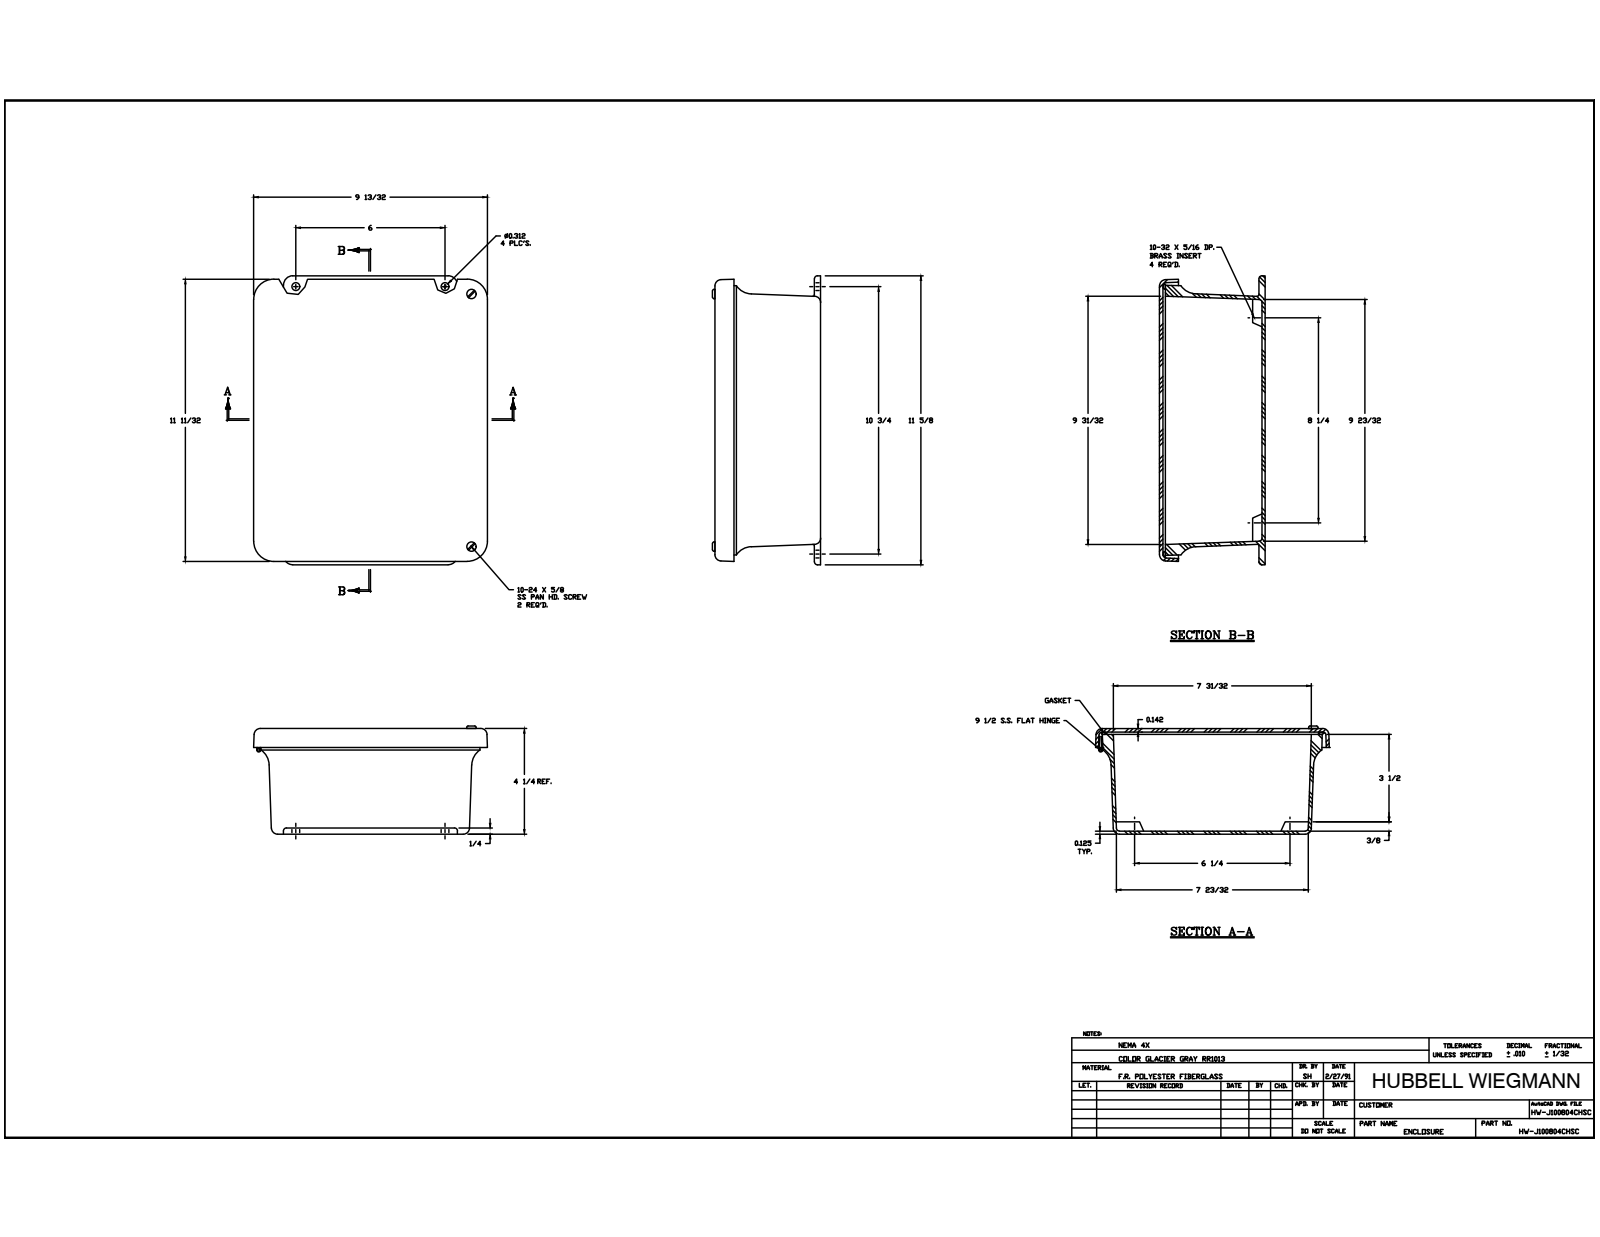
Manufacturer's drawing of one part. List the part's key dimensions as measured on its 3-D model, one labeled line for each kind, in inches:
Part name (STEP PRODUCT): J1008HW_2; RMINS45821P_23; RMINS45821P_24; RMINS45821P_25 (+8 more)
STEP written by: Autodesk Inventor 2014 (AUTOMOTIVE_DESIGN)
Units: inches
Bodies: 22 solids, 759 faces (259 planar, 291 cylindrical, 209 other)
Overall size (bounding box): 11.625 × 9.433 × 4.366
Volume: 60.58 in³ · Surface area: 805.5 in²
Round holes (diameter × count): ⌀0.131 ×8, ⌀0.14 ×8, ⌀0.152 ×5, ⌀0.156 ×4, ⌀0.218 ×4, ⌀0.145 ×2, ⌀0.085 ×1, ⌀0.085 ×1
Round bosses / shafts (diameter × count): ⌀0.25 ×8, ⌀0.125 ×8, ⌀0.27 ×6, ⌀0.19 ×2, ⌀0.156 ×2, ⌀0.155 ×1
Partial cylindrical surfaces — rounded edges, fillets, slot ends (radius × count): R0.031 ×20, R0.125 ×12, R0.25 ×8, R0.2 ×7, R0.375 ×4, R0.75 ×4, R0.063 ×2
Main face-to-face distances: 0.142, 4.093, 4.235, 0.125, 3.968, 4.11, 0.12, 3.89, 0.22, 4.015
Hole centre spacings: 6, 3, 0.25, 2.5, 2.75, 6.25, 1.337, 3.25
